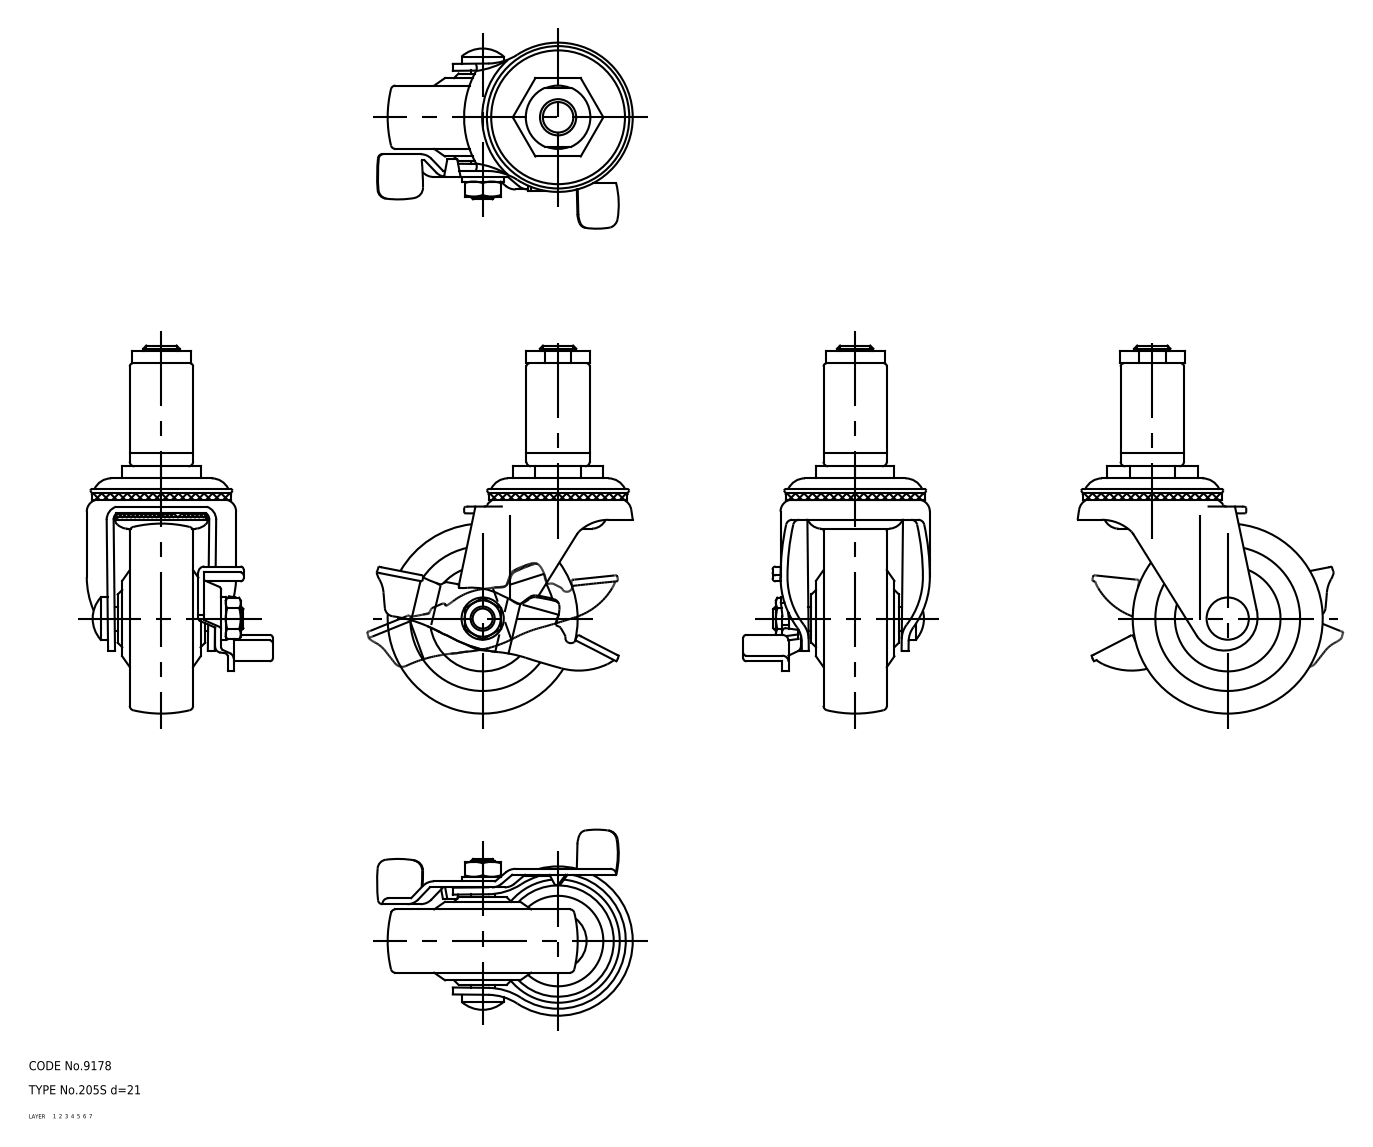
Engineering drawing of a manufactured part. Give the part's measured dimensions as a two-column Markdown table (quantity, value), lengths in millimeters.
| quantity | value |
| --- | --- |
| part name | wheel; main shaft; lever; axle (+1 more) |
| STEP written by | CADfix (AUTOMOTIVE_DESIGN) |
| units | millimeters |
| bodies | 5 solids, 314 faces (0 planar, 0 cylindrical, 314 other) |
| overall size | 122 × 84.88 × 62.14 |
| volume | 110 717 mm³ |
| surface area | 35 298 mm² |
